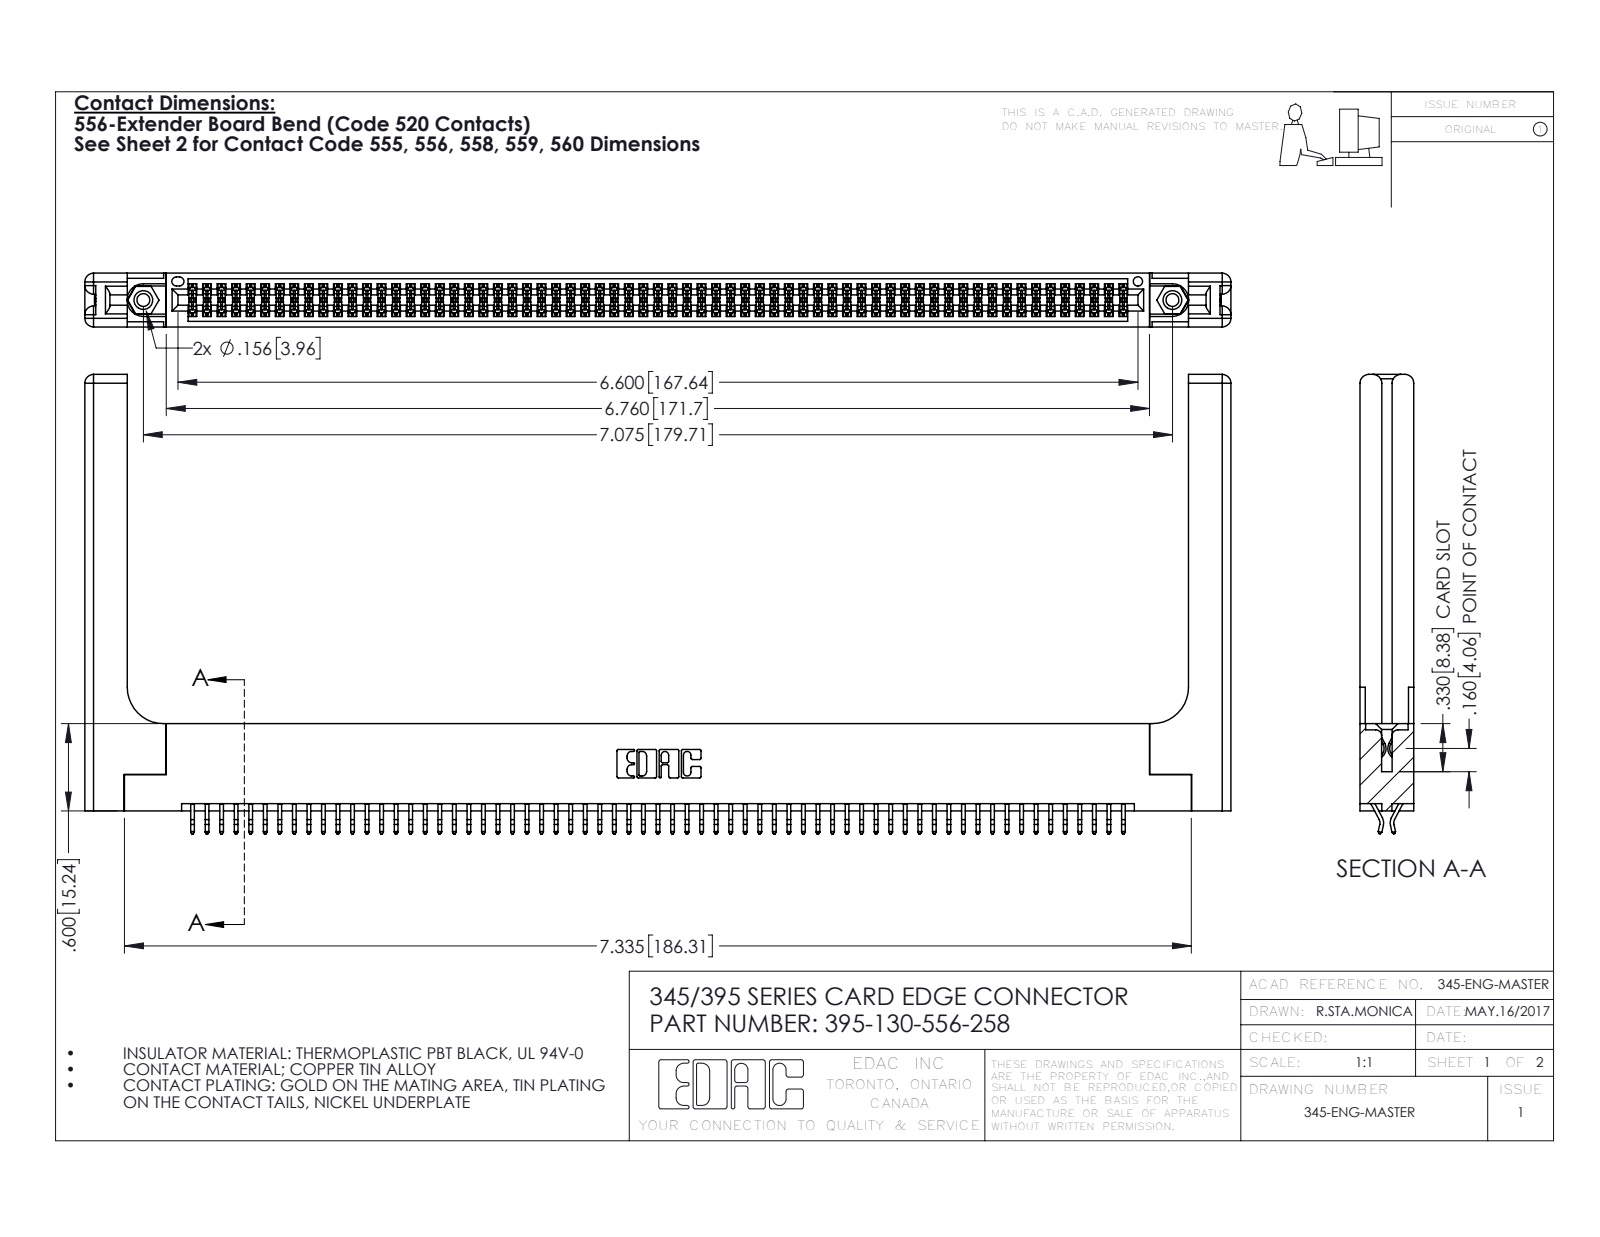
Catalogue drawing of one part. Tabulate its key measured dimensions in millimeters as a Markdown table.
| quantity | value |
| --- | --- |
| part name | 345-292-001_556 Tail; 345-220-058_345-220-058; 395-130-556-258; 345-250-001_345-250-001-102 (+1 more) |
| STEP written by | SolidWorks 2016 (CONFIG_CONTROL_DESIGN) |
| units | millimeters |
| bodies | 135 solids, 7662 faces (5038 planar, 2564 cylindrical, 60 other) |
| overall size | 200.1 × 80.2 × 9.4 |
| volume | 28 120 mm³ |
| surface area | 34 430 mm² |
| round holes (diameter × count) | 2.3 × 2, 3.2 × 2, 4 × 2, 1.6 × 1 |
| round bosses / shafts (diameter × count) | 3.9 × 2 |
| partial cylindrical surfaces (radius × count) | 0.2 × 195, 0.3 × 22, 1.5 × 16, 0.2 × 6, 0.8 × 6, 0.7 × 3, 0.3 × 2, 0.4 × 2 |
| main face-to-face distances | 1.8, 7.6, 9.4, 5.1, 0.6, 2.5, 6.9, 5.7, 3.8, 3.8 |
| hole center spacings | 6.9, 173.7, 179.7 |
